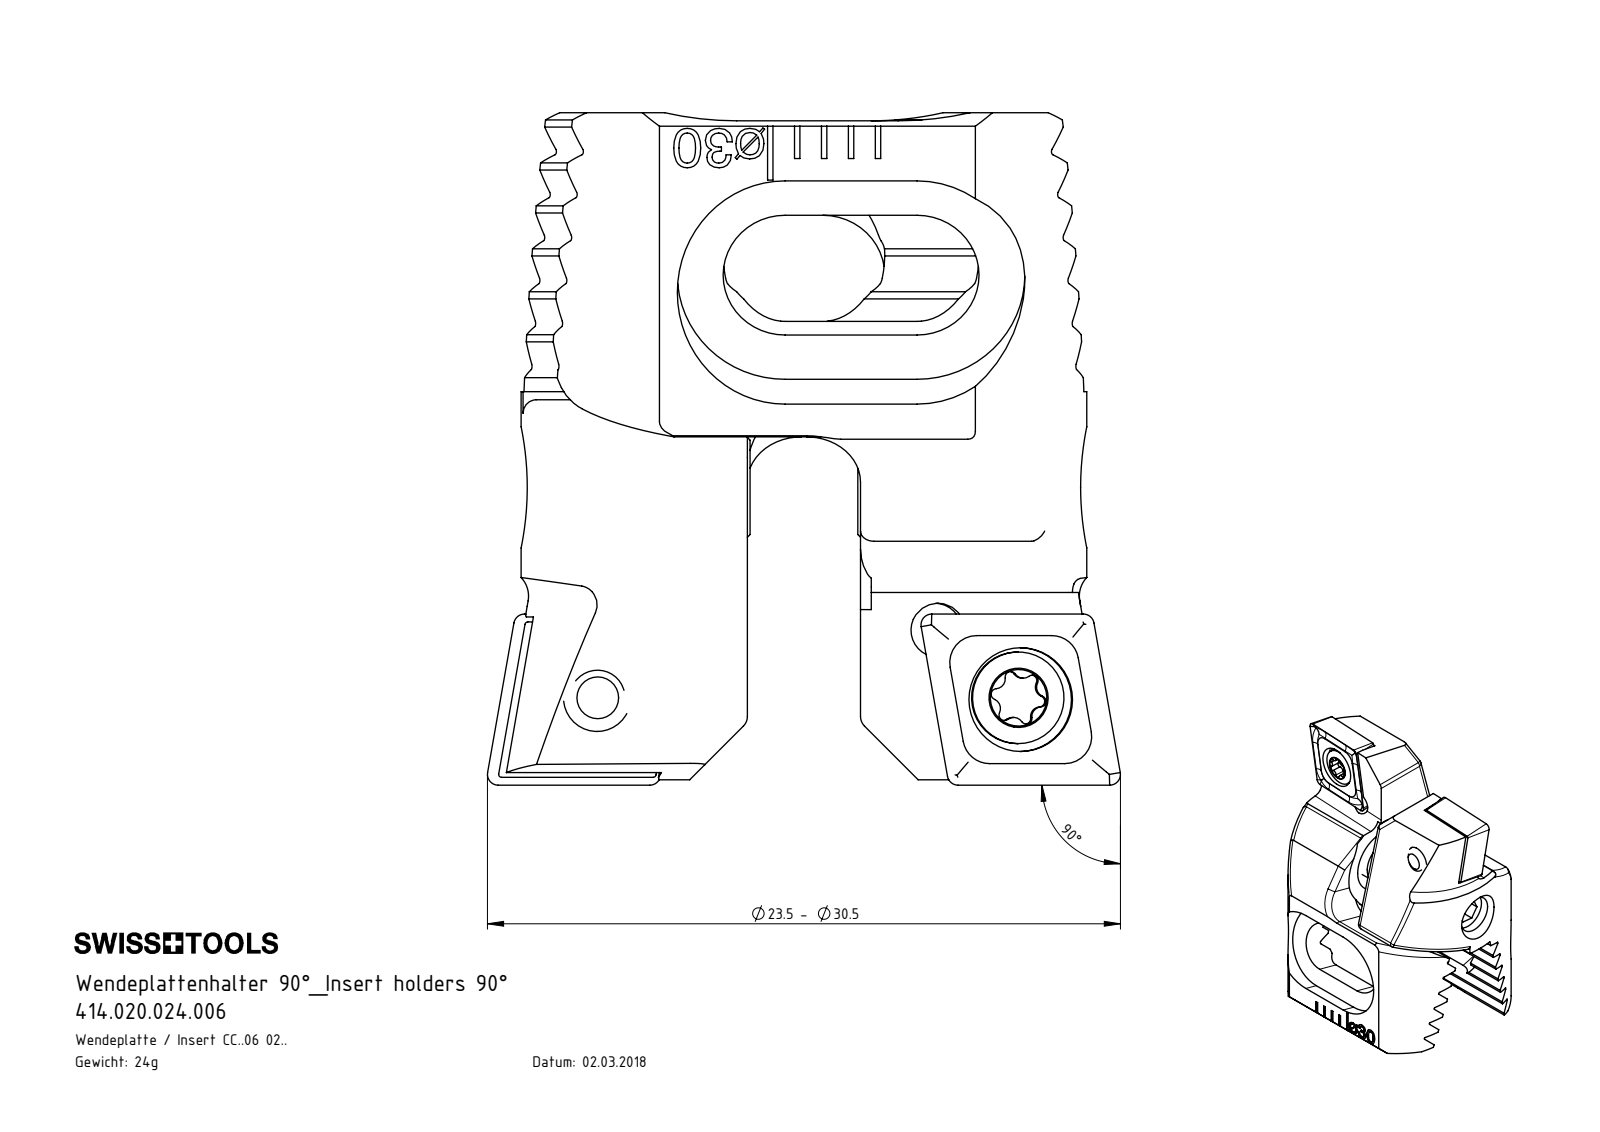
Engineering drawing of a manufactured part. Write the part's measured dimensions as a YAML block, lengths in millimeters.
part_name: "414.020.024.006; WCA-ER2.001.006_A; Z20-xxx.001.015_D; Z20-ER3.001.007_A (+1 more)"
step_written_by: "SolidWorks 2017 (CONFIG_CONTROL_DESIGN)"
units: millimeters
bodies: {solids: 8, faces: 606, planar: 262, cylindrical: 134, other: 210}
overall_size: [24.95, 23.5, 16.2]
volume: 2962
surface_area: 3413
round_holes:
  - {diameter: 1.6, count: 2}
  - {diameter: 2, count: 2}
  - {diameter: 2.05, count: 2}
  - {diameter: 2.8, count: 2}
  - {diameter: 3.85, count: 2}
  - {diameter: 3.5, count: 1}
  - {diameter: 9.1, count: 1}
round_bosses_or_shafts:
  - {diameter: 3.4, count: 2}
  - {diameter: 2.5, count: 2}
  - {diameter: 4, count: 1}
partial_cylinders:
  - {radius: 0.5, count: 16}
  - {radius: 0.12, count: 12}
  - {radius: 0.21, count: 12}
  - {radius: 0.36, count: 10}
  - {radius: 1, count: 4}
  - {radius: 2, count: 4}
  - {radius: 2.3, count: 4}
  - {radius: 4, count: 4}
face_to_face_distances: [1.43, 2.86, 4.29, 3.79, 0.4, 4.6, 5.71, 5.72, 2.97, 6.76]
hole_center_spacings: [3.91, 4.01, 5.5, 13.15, 13.24, 15.98, 9.91, 10.62]
